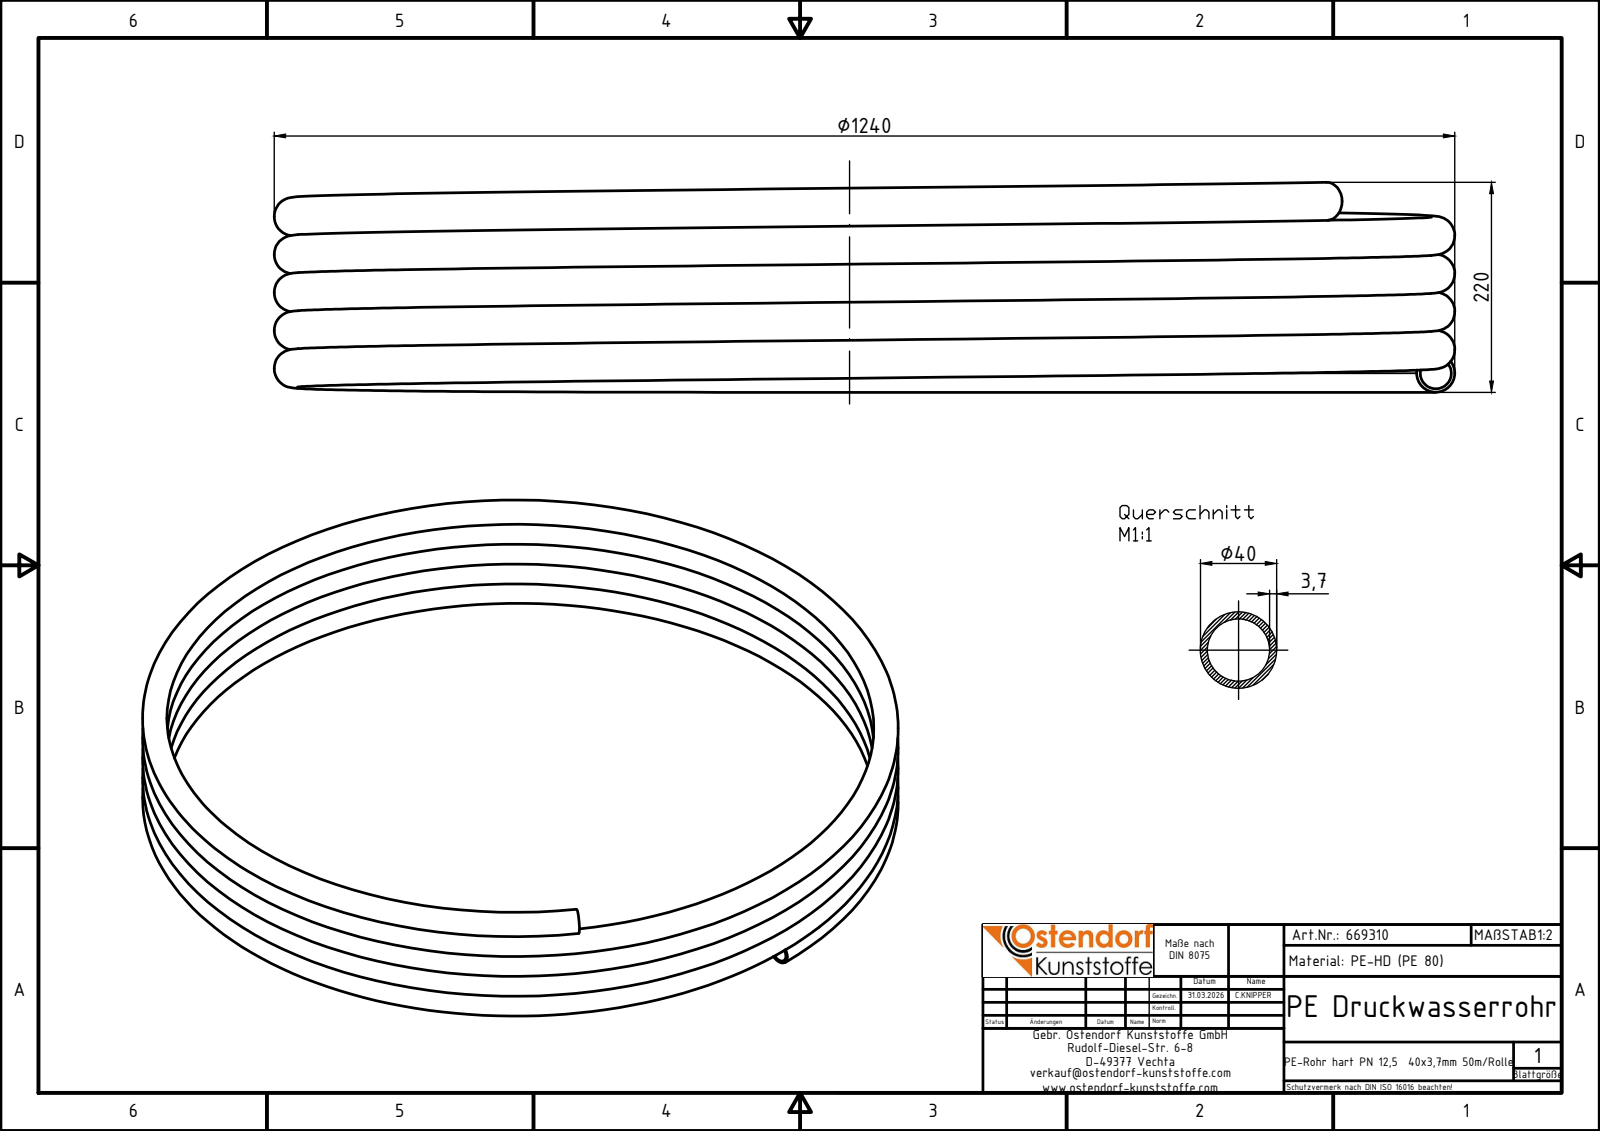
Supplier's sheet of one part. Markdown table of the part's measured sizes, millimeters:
| quantity | value |
| --- | --- |
| part name | 669310z |
| STEP written by | Autodesk Inventor 2024 (AUTOMOTIVE_DESIGN) |
| units | millimeters |
| bodies | 1 solid, 7 faces (3 planar, 0 cylindrical, 4 other) |
| overall size | 1240 × 1240 × 220.55 |
| volume | 7 704 000 mm³ |
| surface area | 4 047 000 mm² |
